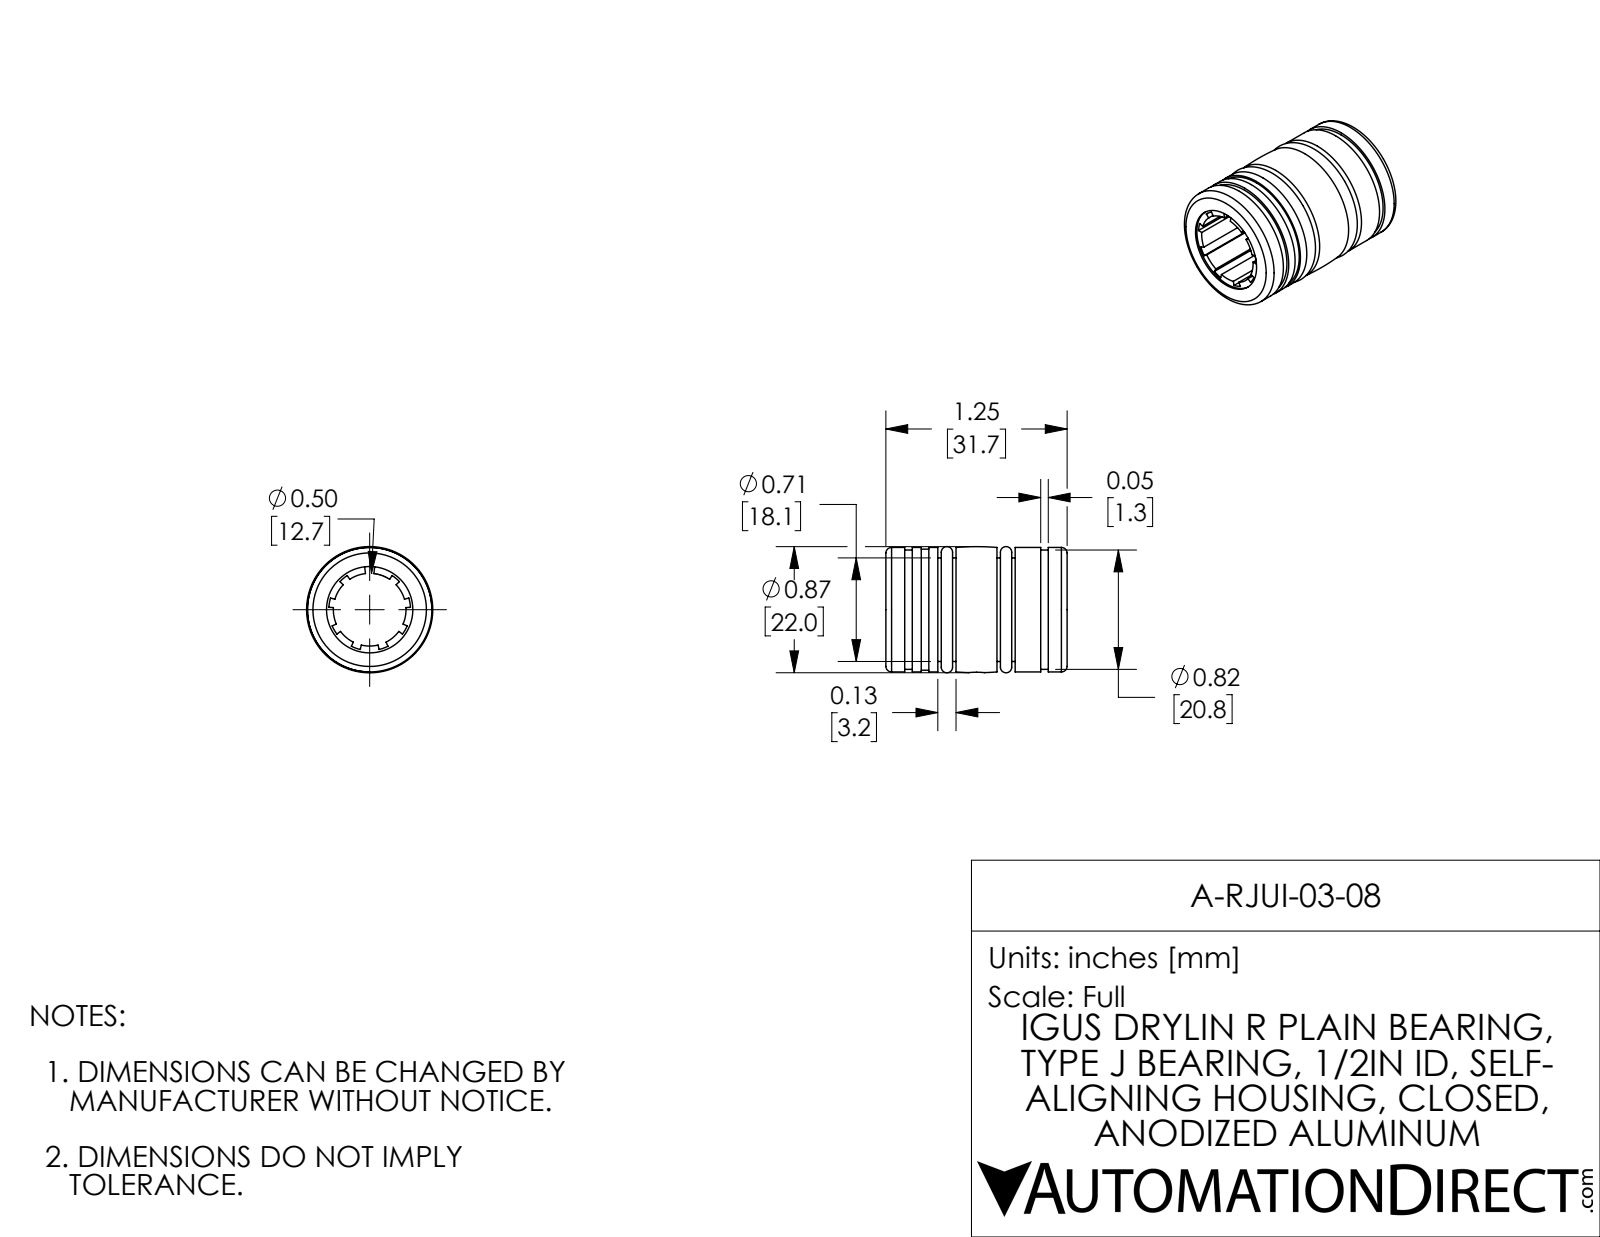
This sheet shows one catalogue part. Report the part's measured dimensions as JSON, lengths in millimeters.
{"part_name": "A-RJUI-03-08", "step_written_by": "SolidWorks 2017 (AUTOMOTIVE_DESIGN)", "units": "millimeters", "bodies": {"solids": 4, "faces": 143, "planar": 69, "cylindrical": 60, "other": 14}, "overall_size": [31.6, 22, 22], "volume_mm3": 6830, "surface_area_mm2": 8748, "round_holes": [[2.8, 1], [15.1, 1], [17, 1]], "round_bosses_or_shafts": [[21.7, 1], [21.1, 1], [20.8, 1], [18.1, 1], [15.1, 1], [2.6, 1]], "partial_cylinders_radius": [[6.4, 1], [7.1, 1], [8.3, 1]], "face_to_face_distances": [5.2, 3.2, 9.1, 22.6, 12.2, 19.4, 10.3, 14.2, 17.4, 8.3]}
